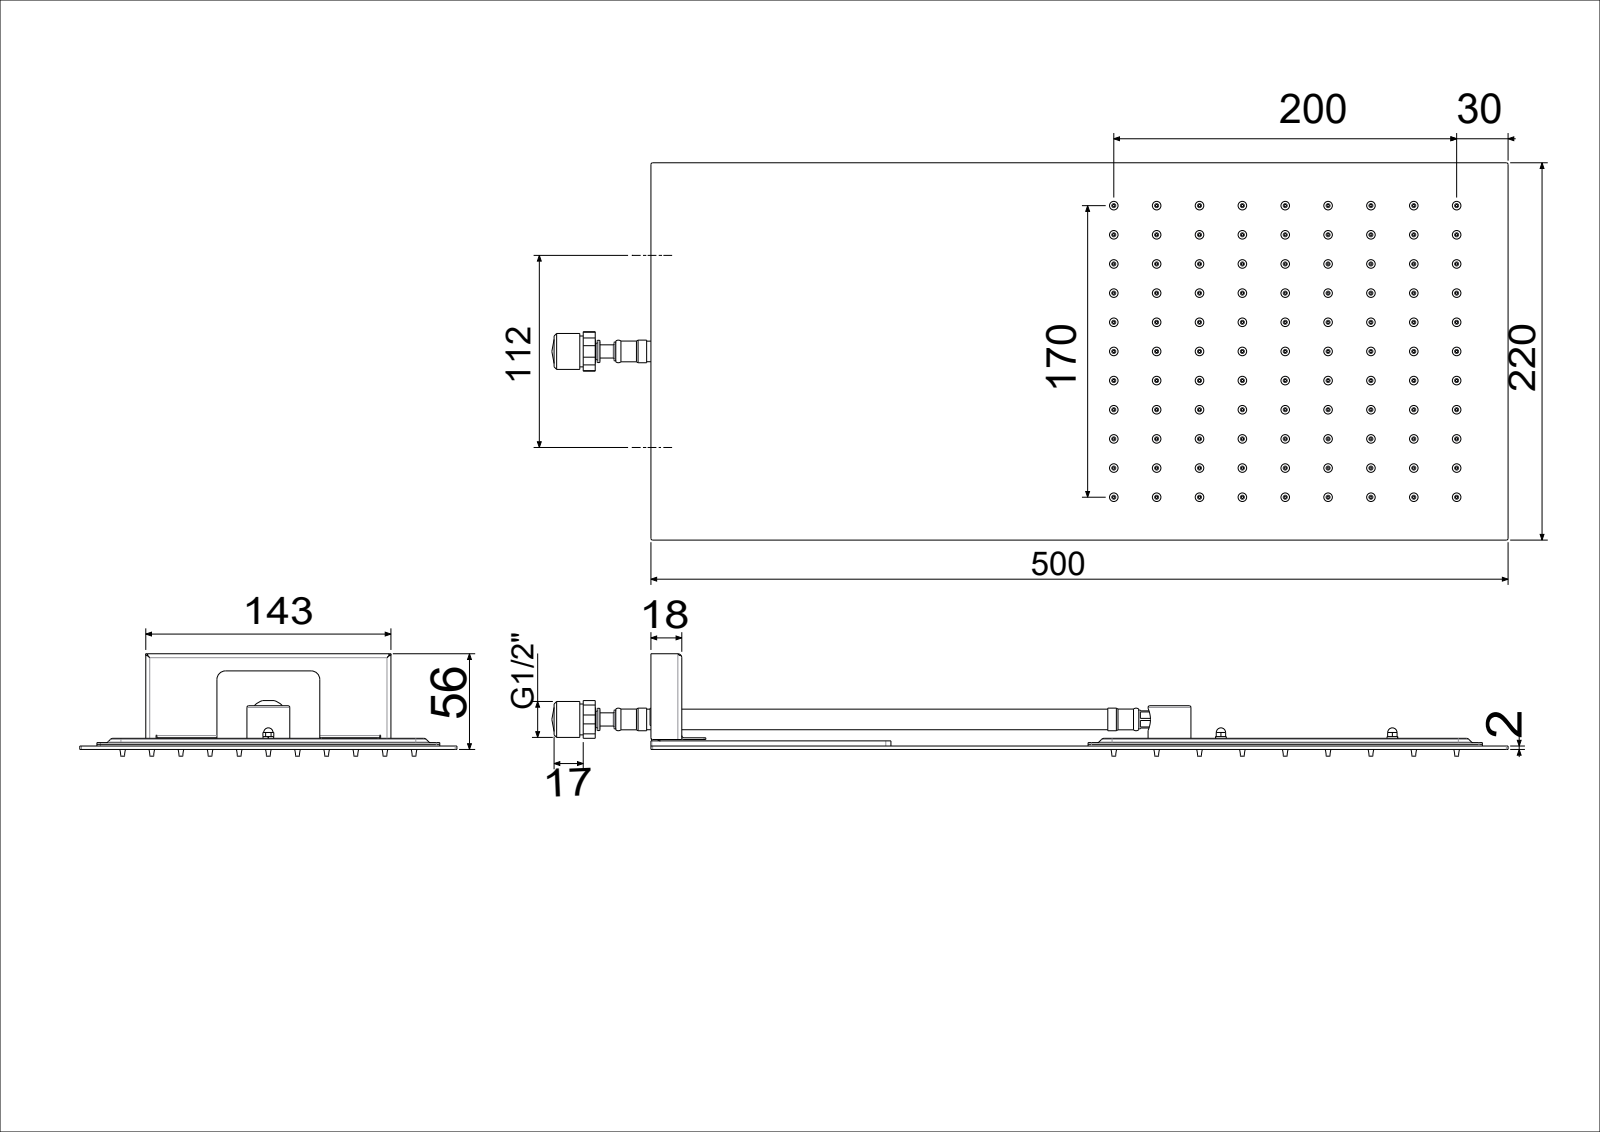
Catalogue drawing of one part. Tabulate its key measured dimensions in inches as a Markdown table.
| quantity | value |
| --- | --- |
| part name | ZSOF117CR |
| STEP written by | CREO PARAMETRIC BY PTC INC, 2020044 (CONFIG_CONTROL_DESIGN) |
| units | inches |
| bodies | 4 solids, 1849 faces (456 planar, 935 cylindrical, 458 other) |
| overall size | 19.685 × 8.661 × 2.354 |
| volume | 24.64 in³ |
| surface area | 582.3 in² |
| round holes (diameter × count) | 0.197 × 101, 0.055 × 99, 0.067 × 99, 0.217 × 3, 0.098 × 2, 0.157 × 2, 0.278 × 2, 0.307 × 2, 0.354 × 2, 0.356 × 2, 0.315 × 1, 0.48 × 1 |
| round bosses / shafts (diameter × count) | 0.394 × 101, 0.35 × 2, 0.276 × 2, 0.236 × 2, 0.984 × 1, 0.866 × 1, 0.52 × 1, 0.476 × 1 |
| partial cylindrical surfaces (radius × count) | 0.039 × 20, 0.079 × 12, 0.118 × 10, 0.02 × 4, 0.051 × 4, 0.091 × 4, 0.128 × 4, 0.01 × 2 |
| main face-to-face distances | 0.039, 0.138, 0.079, 0.118, 0.217, 0.098, 0.177, 0.256, 0.059, 0.02 |
| hole center spacings | 1.19, 2.079, 3.028, 0.984, 1.969, 3.993, 0.669, 2.953 |
